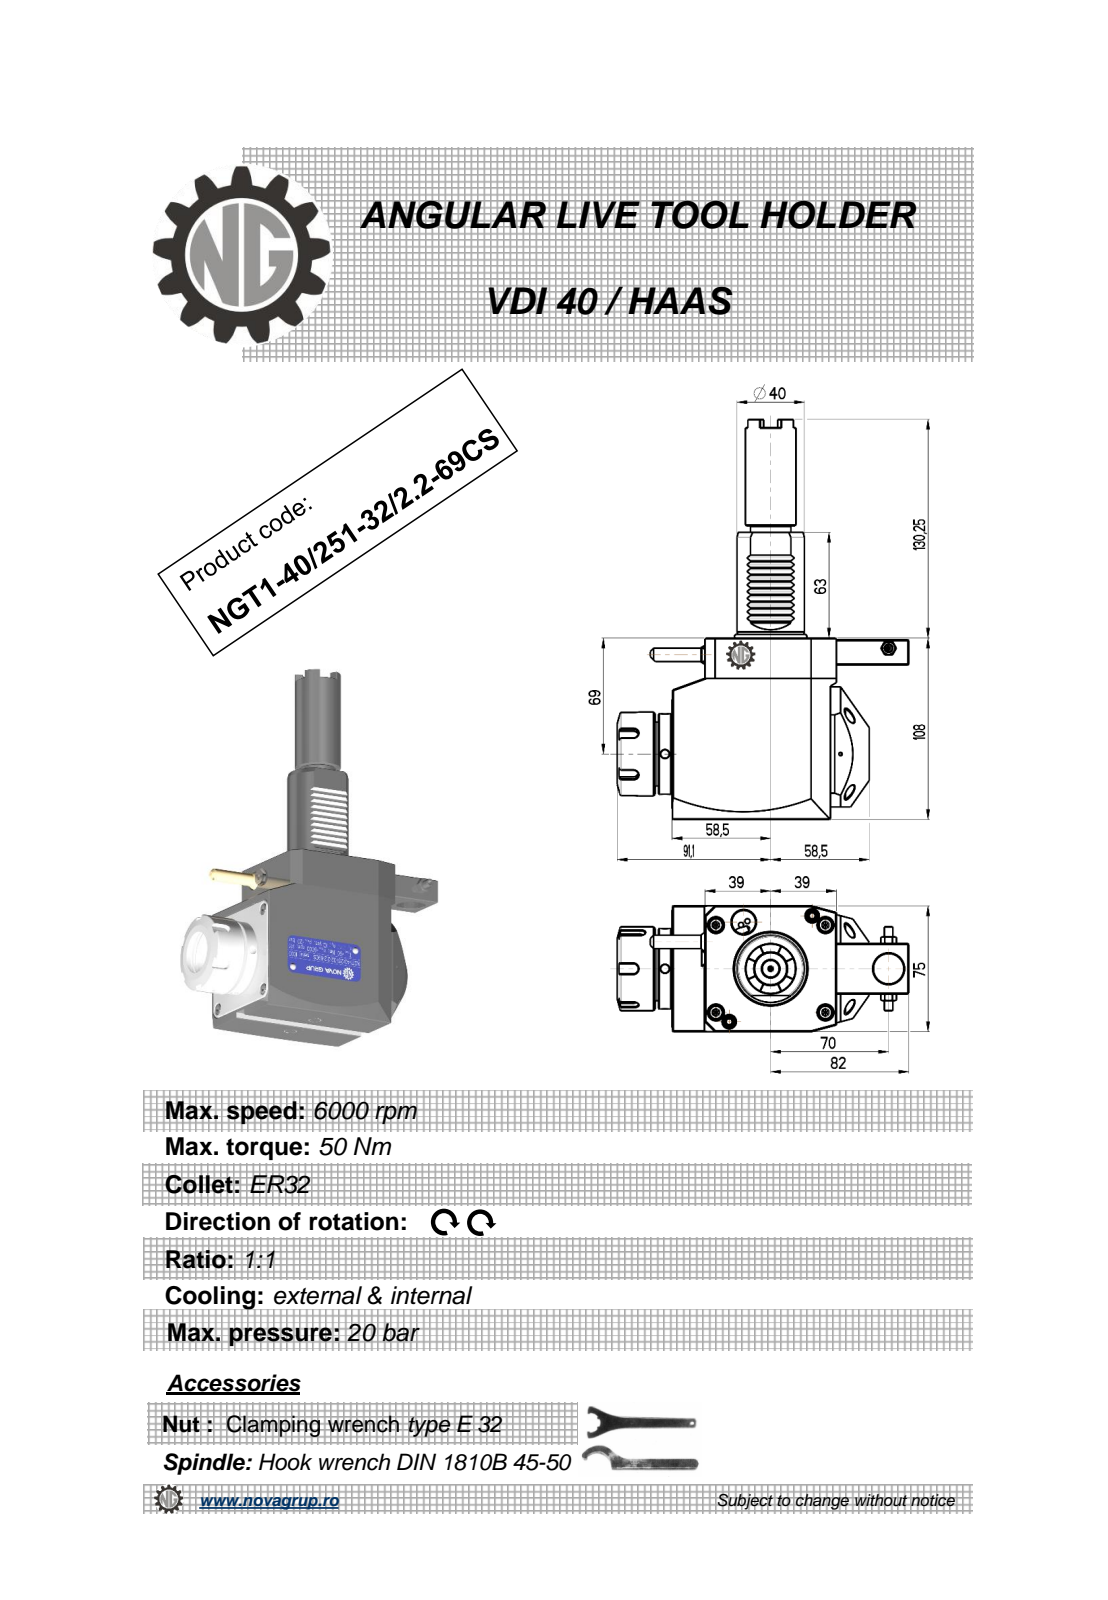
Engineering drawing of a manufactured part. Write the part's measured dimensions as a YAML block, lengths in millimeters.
part_name: "NGT1_40_251_32_2_2_69CS"
step_written_by: "PRO/ENGINEER BY PARAMETRIC TECHNOLOGY CORPORATION, 2010280 (CONFIG_CONTROL_DESIGN)"
units: millimeters
bodies: {solids: 1, faces: 481, planar: 240, cylindrical: 98, other: 143}
overall_size: [238.25, 173.1, 76.6]
volume: 971877
surface_area: 81906
round_holes:
  - {diameter: 5, count: 3}
  - {diameter: 3, count: 1}
  - {diameter: 4.2, count: 1}
  - {diameter: 9.5, count: 1}
  - {diameter: 18, count: 1}
  - {diameter: 19.5, count: 1}
  - {diameter: 27, count: 1}
round_bosses_or_shafts:
  - {diameter: 50, count: 1}
  - {diameter: 48, count: 1}
  - {diameter: 41.5, count: 1}
  - {diameter: 41, count: 1}
  - {diameter: 40, count: 1}
  - {diameter: 30, count: 1}
  - {diameter: 24, count: 1}
  - {diameter: 10, count: 1}
partial_cylinders:
  - {radius: 0.26, count: 12}
  - {radius: 0.3, count: 10}
  - {radius: 0.2, count: 6}
  - {radius: 3, count: 5}
  - {radius: 5.8, count: 2}
  - {radius: 6, count: 2}
  - {radius: 600, count: 2}
  - {radius: 0.5, count: 1}
face_to_face_distances: [75, 108, 19.5, 97.5, 1, 3.5, 22.5, 78, 19.3, 97.3]
hole_center_spacings: [16.19, 61.13, 61.5, 62.75, 70, 132.75, 146.94]
